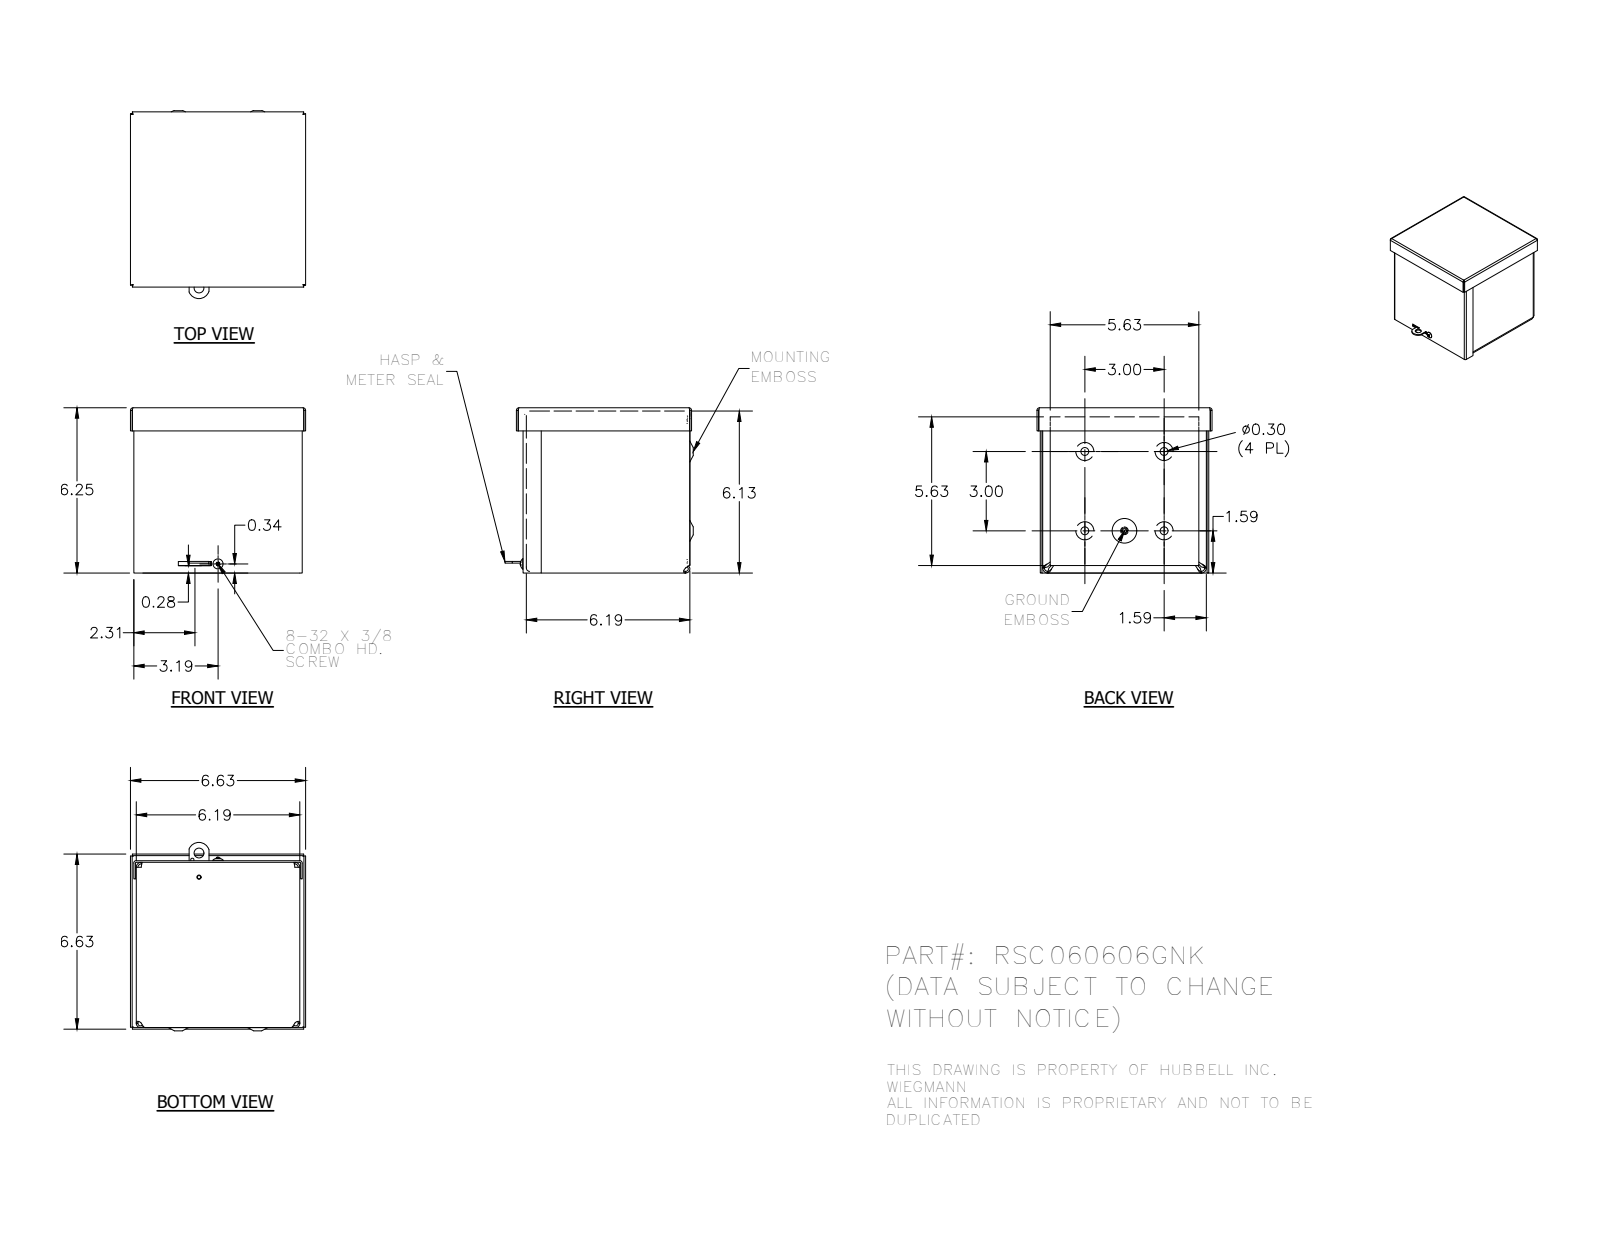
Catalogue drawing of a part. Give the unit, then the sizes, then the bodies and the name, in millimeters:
Units: millimetres
Overall size (bounding box): 180.97 × 168.28 × 158.76
Round holes (diameter × count): ⌀7.62 ×4, ⌀3.17 ×2, ⌀7.95 ×2, ⌀3.76 ×1, ⌀3.96 ×1, ⌀4.19 ×1, ⌀9.52 ×1
Round bosses / shafts (diameter × count): ⌀9.75 ×1, ⌀5.8 ×1, ⌀4.17 ×1
Partial cylindrical surfaces — rounded edges, fillets, slot ends (radius × count): R0.79 ×8, R2.37 ×8, R3.17 ×8, R4.75 ×8, R1.4 ×4, R1.57 ×4, R2.38 ×4, R2.97 ×4
Main face-to-face distances: 1.58, 155.59, 1.57, 157.17, 158.74, 3.15, 157.16, 158.73, 154.01, 157.15
Hole centre spacings: 76.2, 38.1, 85.19, 107.76, 9.1, 17.84, 23.19, 31.79
Volume: 330 011 mm³ · Surface area: 426 094 mm²
Bodies: 6 solids, 347 faces (153 planar, 73 cylindrical, 121 other)
Part name (STEP PRODUCT): RSC060606GNK_WRAP; RSC0606GNK_LID; RSC0606GNK_CAP; 3183 (+3 more)
STEP written by: Autodesk Inventor 2014 (AUTOMOTIVE_DESIGN)
